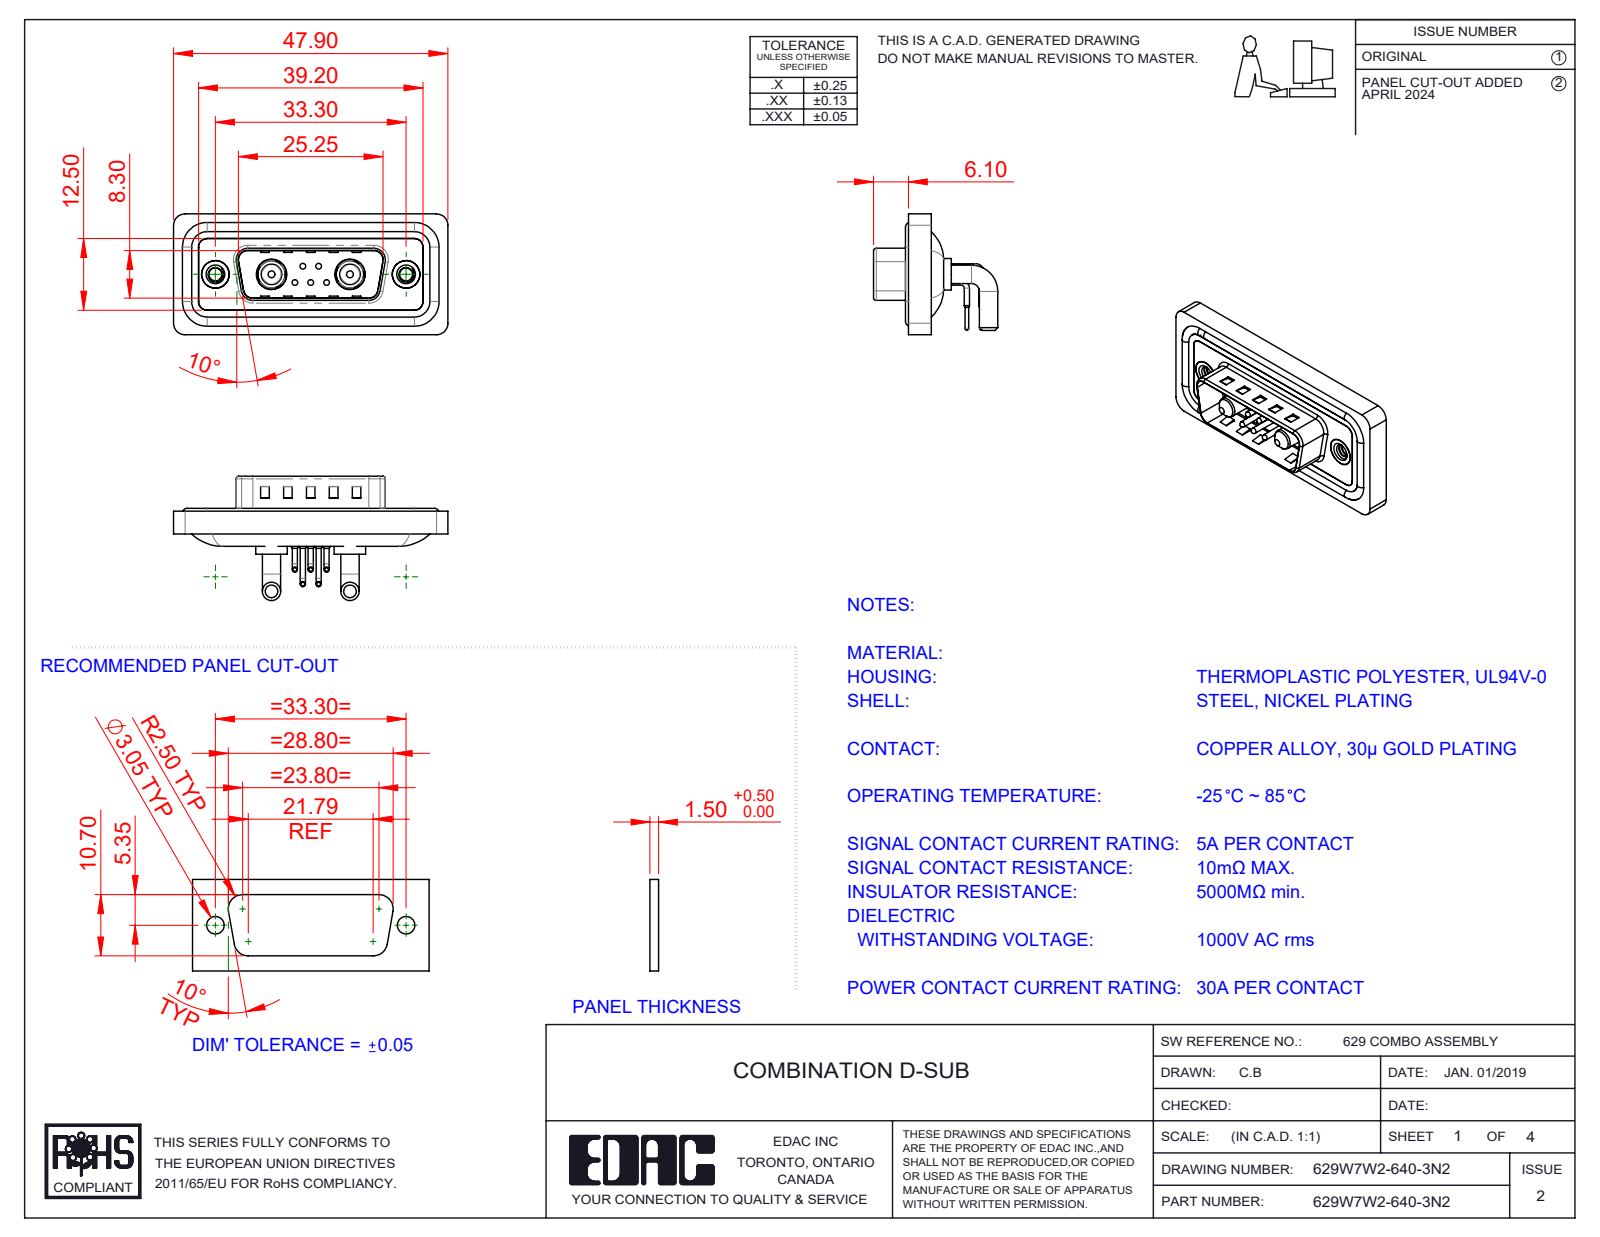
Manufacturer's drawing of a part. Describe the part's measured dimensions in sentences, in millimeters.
The part is named "629Combo Contact Row 2; 629Combo Threaded Rivet_2; 629Combo Waterproof Housing_15 Contacts; 629Combo Shell Front_15 Contacts (+5 more)". Its 3-D file was written by "SolidWorks 2023 (CONFIG_CONTROL_DESIGN)". It is 16 solids with 1083 faces: 517 planar, 406 cylindrical and 160 other. Overall it measures 47.9 by 21.7 by 21.1 millimeters. Its volume is 5 748 cubic millimeters and its surface area 9 178 square millimeters. Round holes: 5 of diameter 0.75, 5 of diameter 1.6, 5 of diameter 2, 2 of diameter 2.26, 2 of diameter 4, 2 of diameter 4.8, 2 of diameter 4.85, 2 of diameter 5, 2 of diameter 5.3. Round bosses or shafts: 10 of diameter 0.9, 5 of diameter 1.5, 5 of diameter 1, 5 of diameter 0.65, 4 of diameter 3.2, 4 of diameter 1.6, 2 of diameter 5.5, 2 of diameter 5.2. Partial cylindrical surfaces (rounded edges, fillets, slot ends): 20 of radius 2, 18 of radius 1.5, 8 of radius 0.5, 8 of radius 1.6, 5 of radius 1.01, 4 of radius 0.25, 4 of radius 0.6, 4 of radius 0.65. The main face-to-face distances are 0.4, 2.9, 0.8, 1.1, 2.1, 1.6, 2.5, 3.1, 4.5, 4.1. The hole center spacings are 3.16, 2.77, 9.8, 23.5, 4.31, 4.33, 5.03, 5.04.
